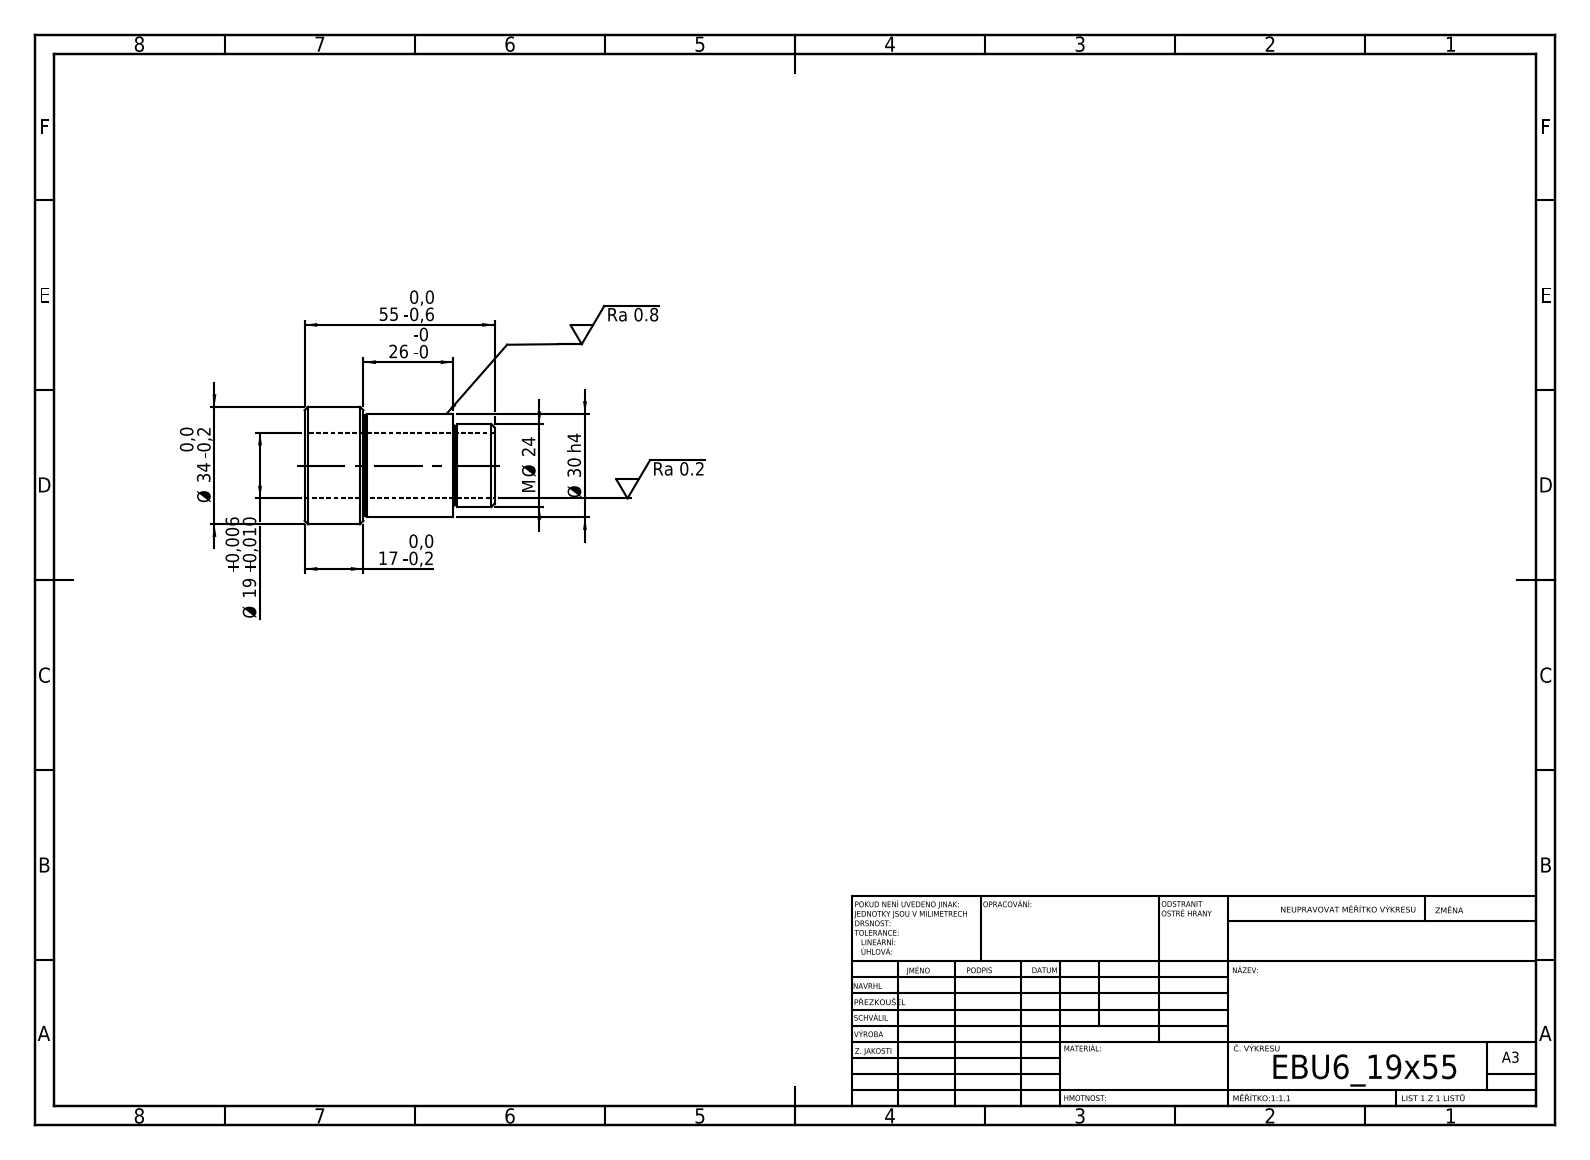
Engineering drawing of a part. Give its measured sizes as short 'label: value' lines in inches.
written by: SolidWorks 2019 (CONFIG_CONTROL_DESIGN)
unit: in
bodies: 1 solid, 27 faces (5 planar, 12 cylindrical, 10 other)
size: 2.165 × 1.339 × 1.339
volume: 1.43 in³; area: 14.97 in²
holes: 1× ⌀0.748
bosses: 1× ⌀1.339, 1× ⌀1.181, 1× ⌀1.142, 1× ⌀0.945, 1× ⌀0.906
face distances: 1.693, 1.024, 0.669, 0.472, 1.496, 2.165, 0.433, 0.039, 1.063, 1.732
